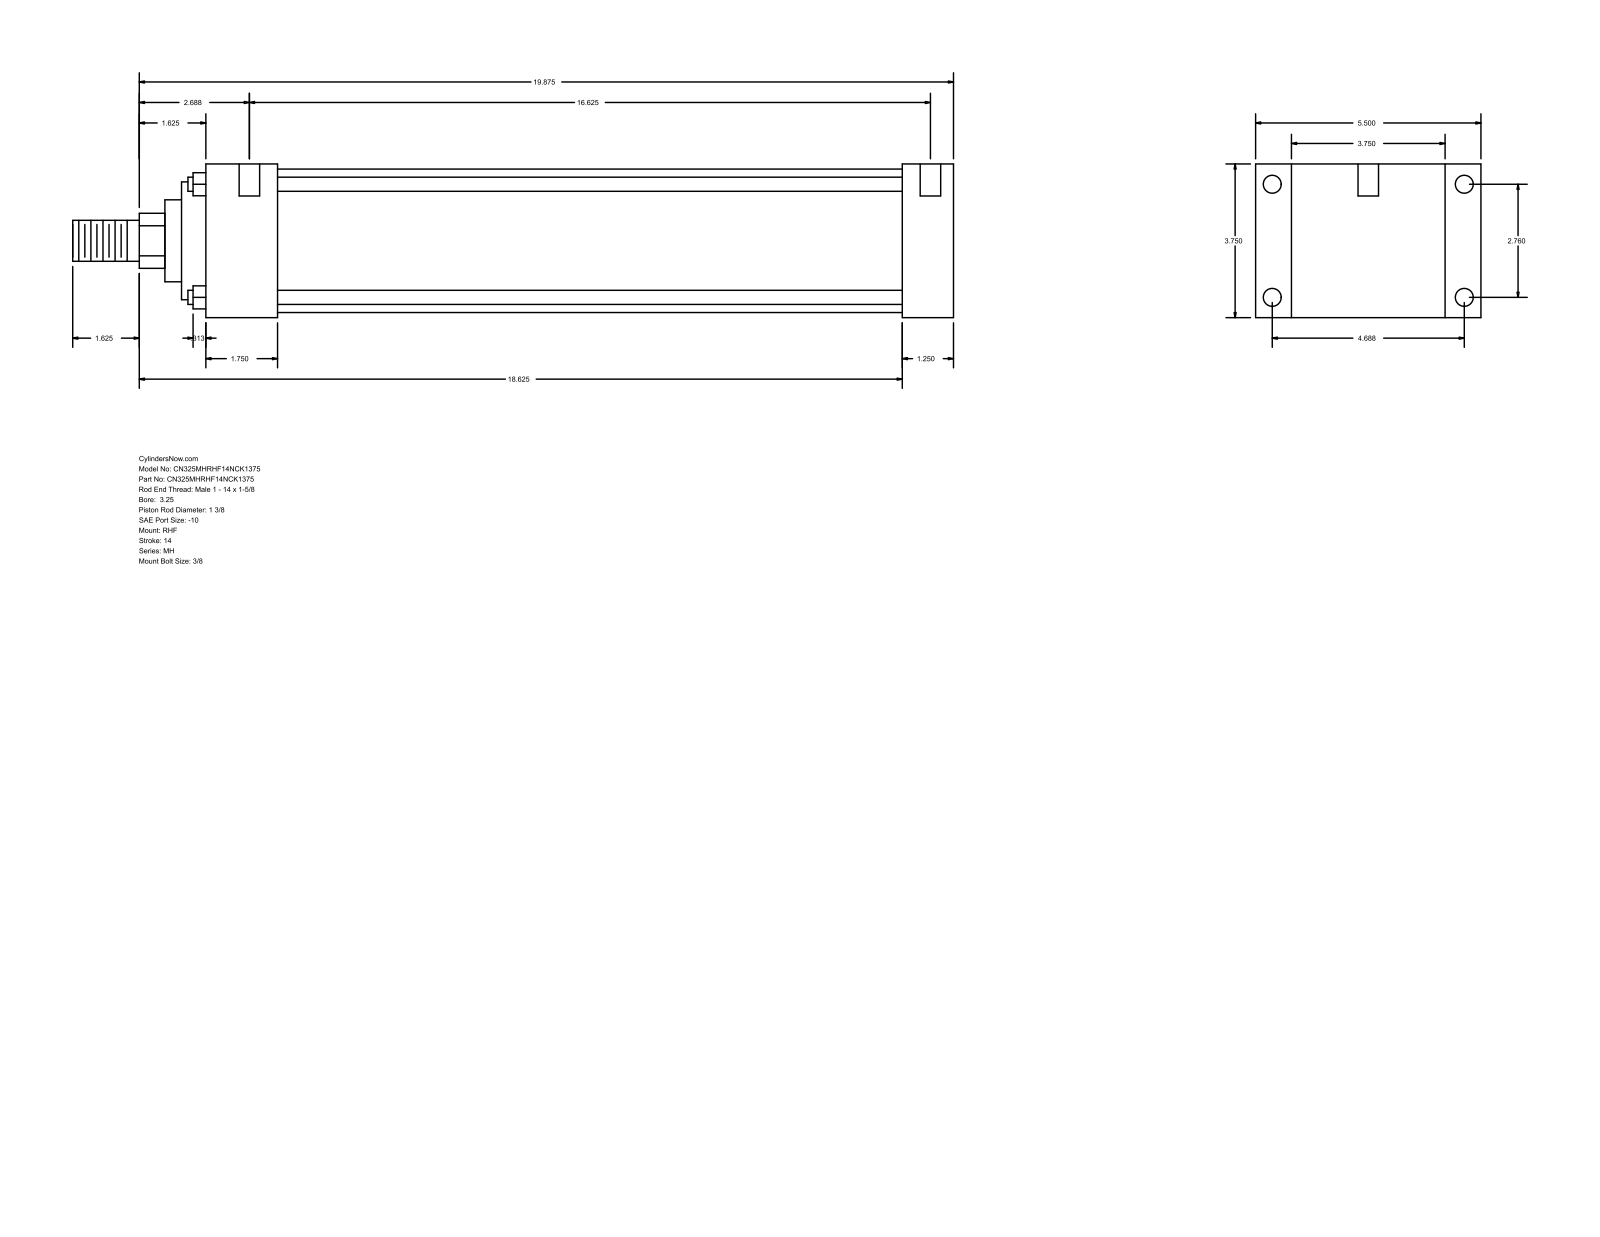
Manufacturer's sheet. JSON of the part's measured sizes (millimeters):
{"part_name": "MH_RHF__0325_1.375", "step_written_by": "GSSL Pune (CONFIG_CONTROL_DESIGN)", "units": "millimeters", "bodies": {"solids": 0, "faces": 90, "planar": 61, "cylindrical": 29, "other": 0}, "overall_size": [546.1, 139.7, 95.25], "round_holes": [[5.56, 4], [11.13, 4], [12.7, 2]], "round_bosses_or_shafts": [[8.76, 4], [88.9, 1], [73.03, 1], [50.8, 1], [34.92, 1], [25.4, 1]], "partial_cylinders_radius": [[17.06, 1]], "face_to_face_distances": [95.24, 31.75, 22.23, 117.47, 431.8, 463.55, 139.7, 44.45, 387.35, 419.1], "hole_center_spacings": [70.1, 119.06, 138.16, 428.63, 1.59, 4.76, 422.28, 423.87]}
